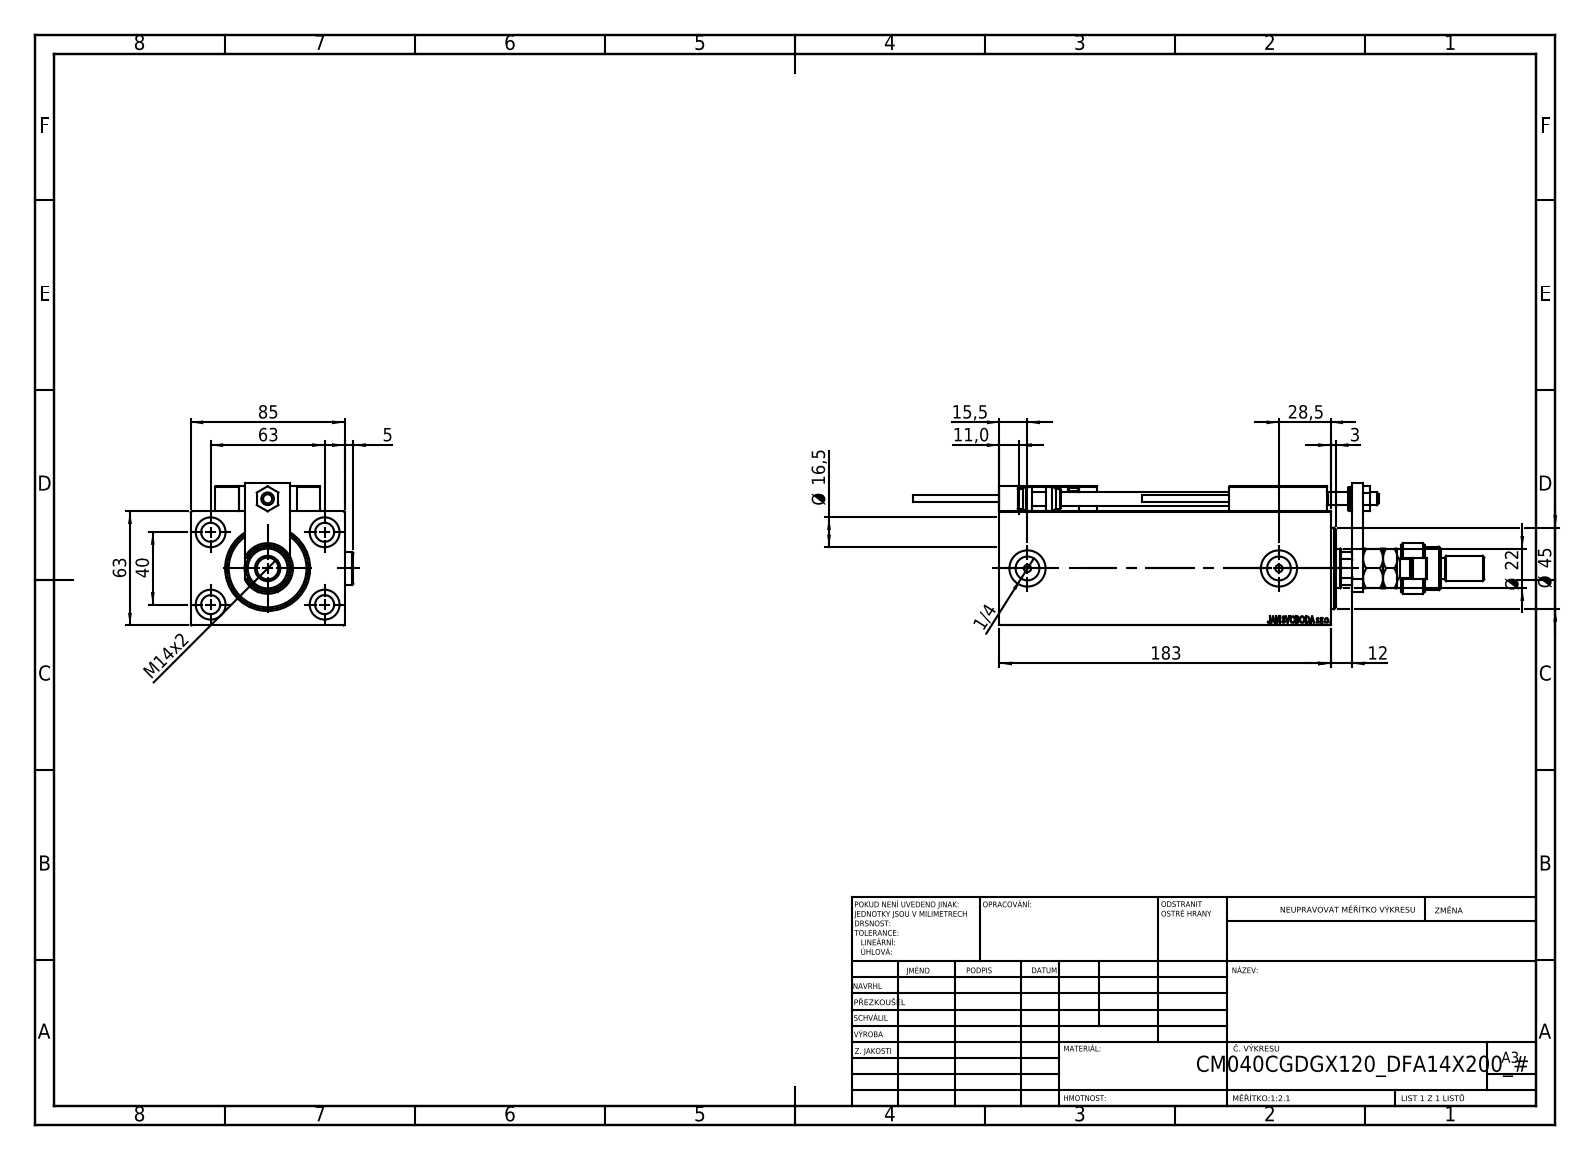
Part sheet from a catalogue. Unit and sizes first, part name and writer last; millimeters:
Units: millimetres
Overall size (bounding box): 316 × 89.9 × 78.5
Round holes (diameter × count): ⌀4 ×6, ⌀8 ×5, ⌀16.5 ×5, ⌀3.2 ×4, ⌀10.5 ×4, ⌀5 ×2, ⌀13.16 ×2, ⌀20 ×2, ⌀7 ×1, ⌀12.5 ×1, ⌀22 ×1, ⌀25.5 ×1
Round bosses / shafts (diameter × count): ⌀18 ×3, ⌀11 ×2, ⌀5 ×2, ⌀3.8 ×2, ⌀28 ×1, ⌀24 ×1, ⌀14 ×1, ⌀13 ×1
Partial cylindrical surfaces — rounded edges, fillets, slot ends (radius × count): R0.3 ×30, R3 ×2, R9.75 ×1, R10.5 ×1
Main face-to-face distances: 63, 85, 12, 171, 183, 14, 30, 18, 77, 6
Hole centre spacings: 37.31, 11.37, 20, 29.59, 29.69, 36.06, 36.53, 40
Volume: 875 030 mm³ · Surface area: 174 192 mm²
Bodies: 27 solids, 1421 faces (622 planar, 217 cylindrical, 582 other)
Part name (STEP PRODUCT): FEMALE_PART_FOR_DFA; KONCOVKA; ZARAZKA; X_Y_DFA (+7 more)
STEP written by: SolidWorks 2019 (CONFIG_CONTROL_DESIGN)
